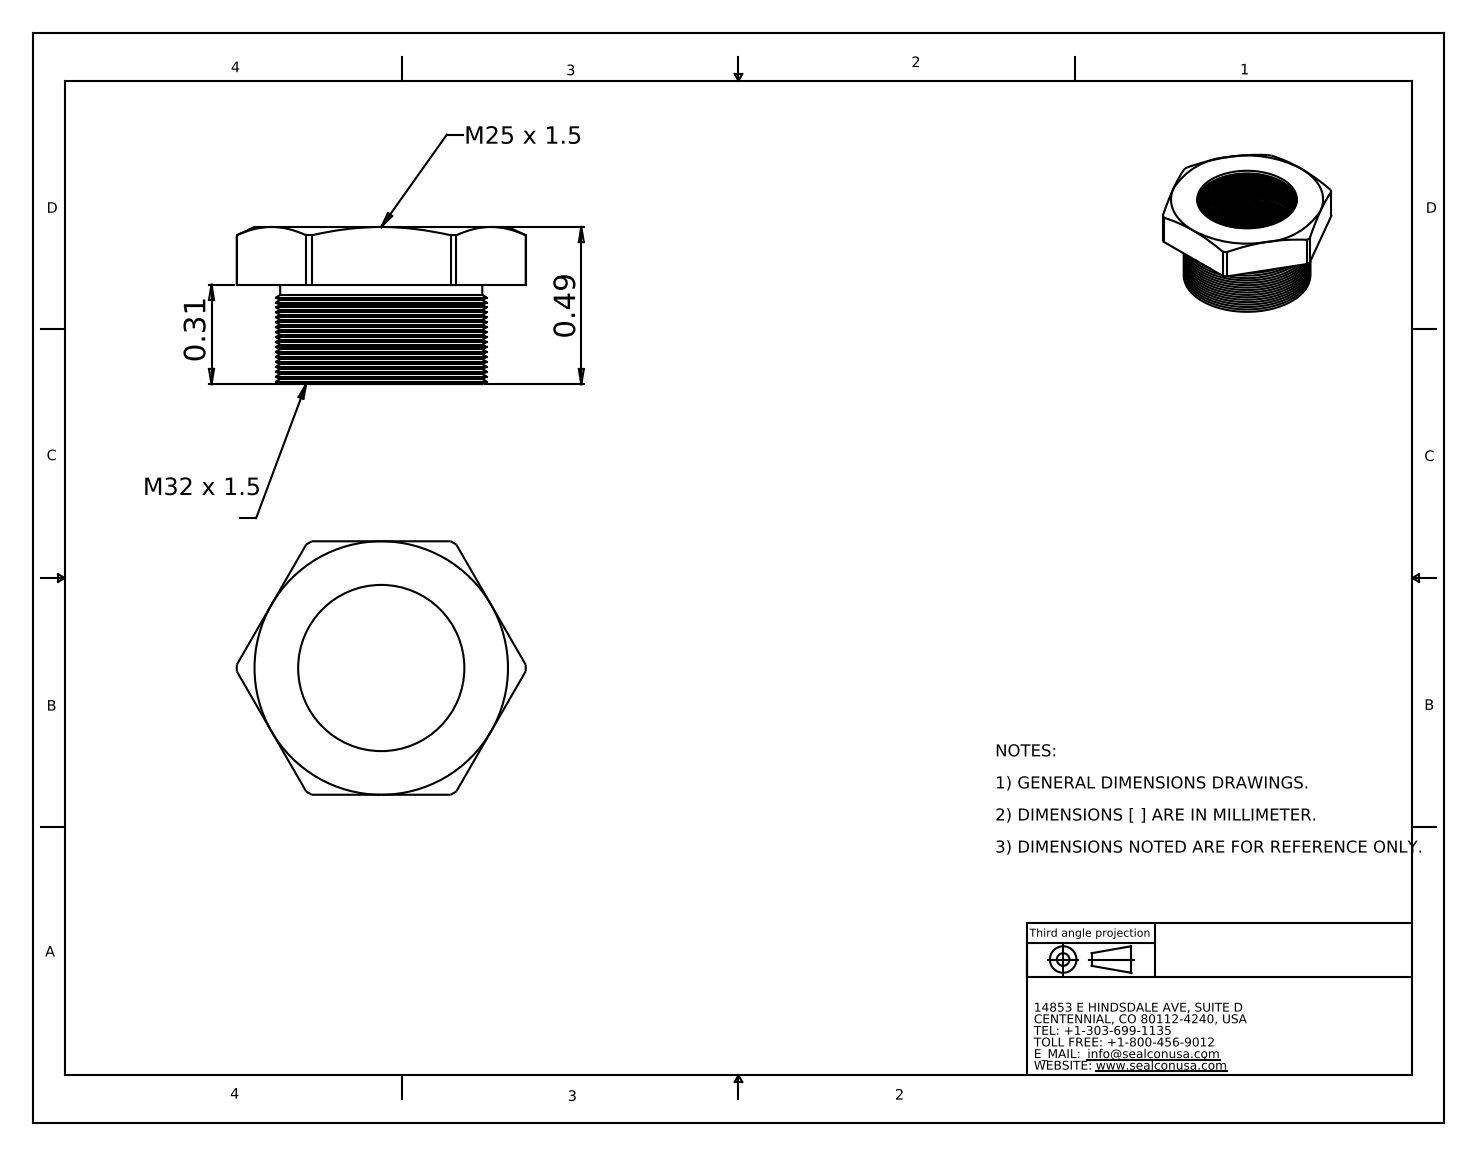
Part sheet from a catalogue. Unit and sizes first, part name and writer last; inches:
Units: inches
Overall size (bounding box): 0.901 × 0.79 × 0.49
Round holes (diameter × count): ⌀0.518 ×1
Round bosses / shafts (diameter × count): ⌀0.63 ×1
Partial cylindrical surfaces — rounded edges, fillets, slot ends (radius × count): R0.45 ×1
Main face-to-face distances: 0.18, 0.79, 0.31, 0.49
Volume: 0.092 in³ · Surface area: 3.933 in²
Bodies: 1 solid, 281 faces (9 planar, 73 cylindrical, 199 other)
Part name (STEP PRODUCT): RM-3225-SS
STEP written by: SolidWorks 2008 (CONFIG_CONTROL_DESIGN)
